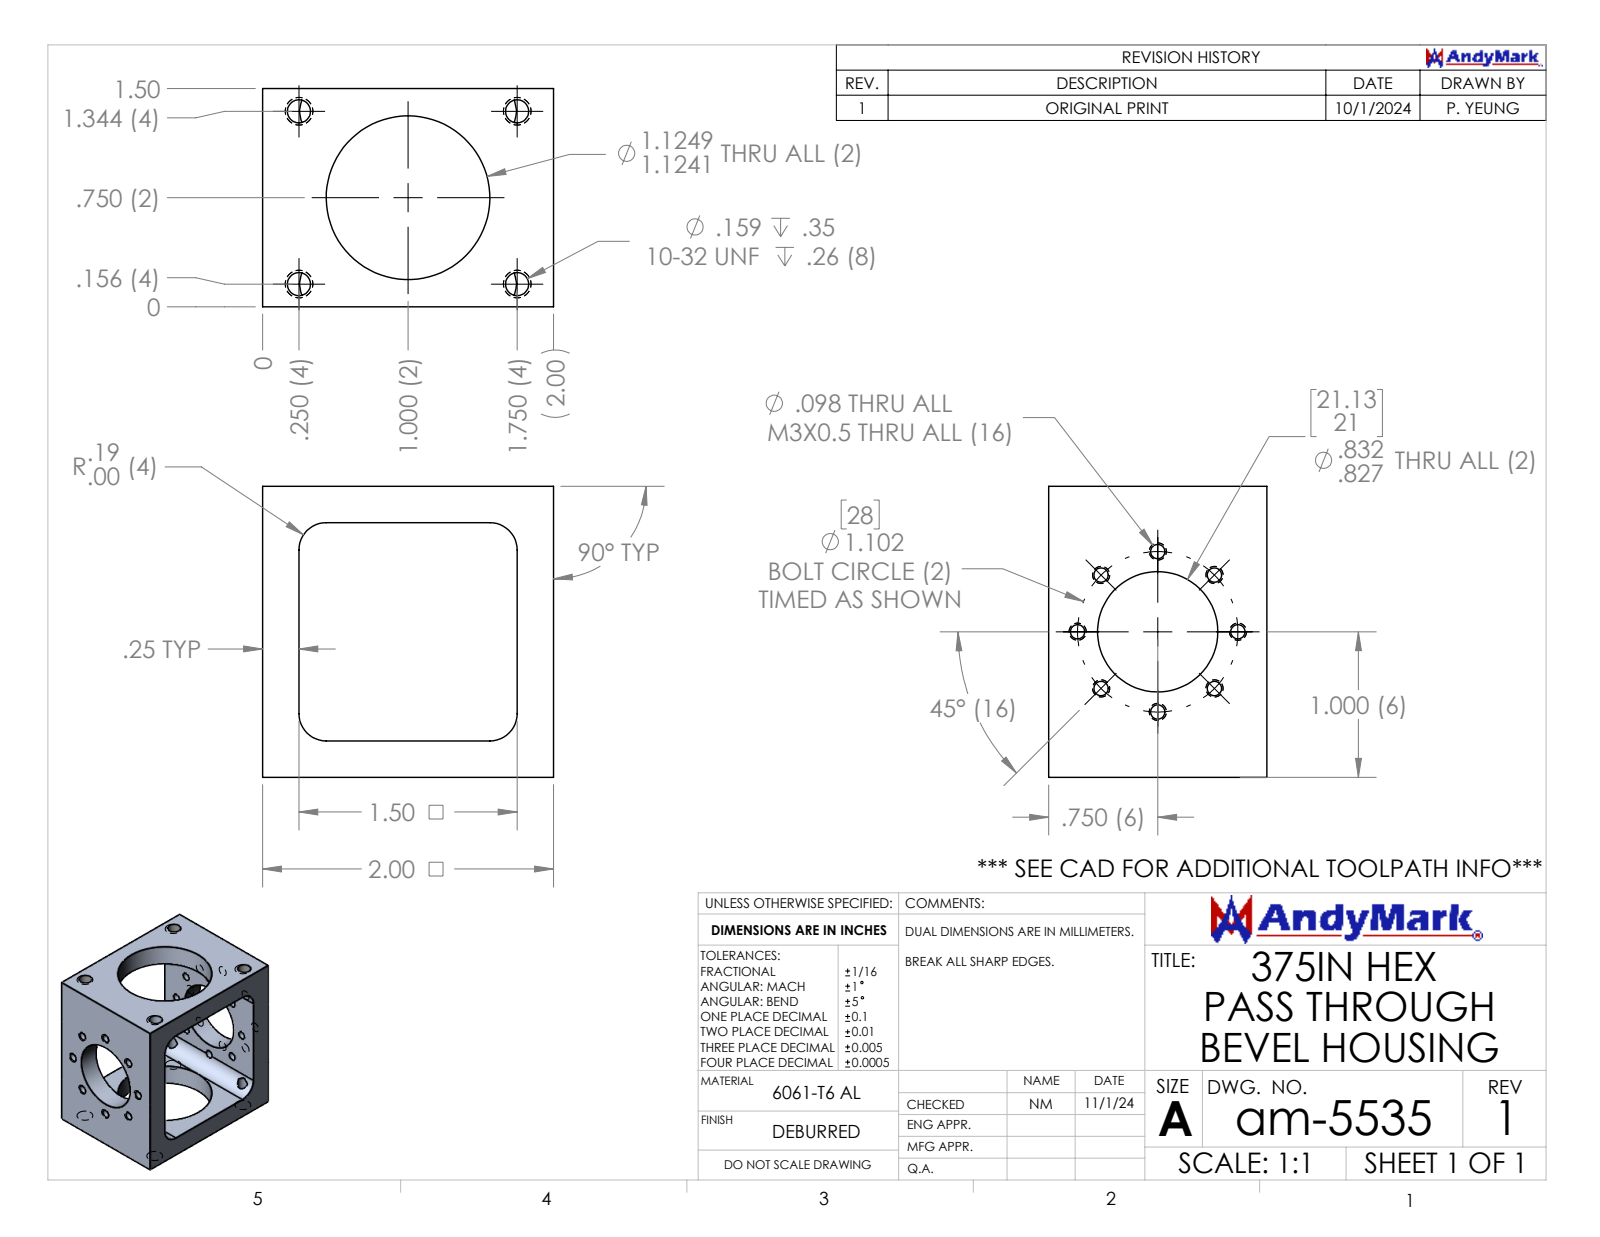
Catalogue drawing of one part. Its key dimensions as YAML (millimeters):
part_name: "am-5535 375H Pass Through Bevel Housing"
step_written_by: "SolidWorks 2024 (AUTOMOTIVE_DESIGN)"
units: millimeters
bodies: {solids: 1, faces: 88, planar: 12, cylindrical: 60, other: 16}
overall_size: [50.8, 50.8, 38.1]
volume: 29790
surface_area: 14950
round_holes:
  - {diameter: 2.5, count: 8}
  - {diameter: 4, count: 4}
  - {diameter: 21, count: 1}
  - {diameter: 28.6, count: 1}
partial_cylinders:
  - {radius: 4.7, count: 4}
face_to_face_distances: [50.8, 6.4, 44.5, 38.1]
hole_center_spacings: [10.7, 14, 19.8, 25.9, 24.3, 28, 30.1, 38.1]
